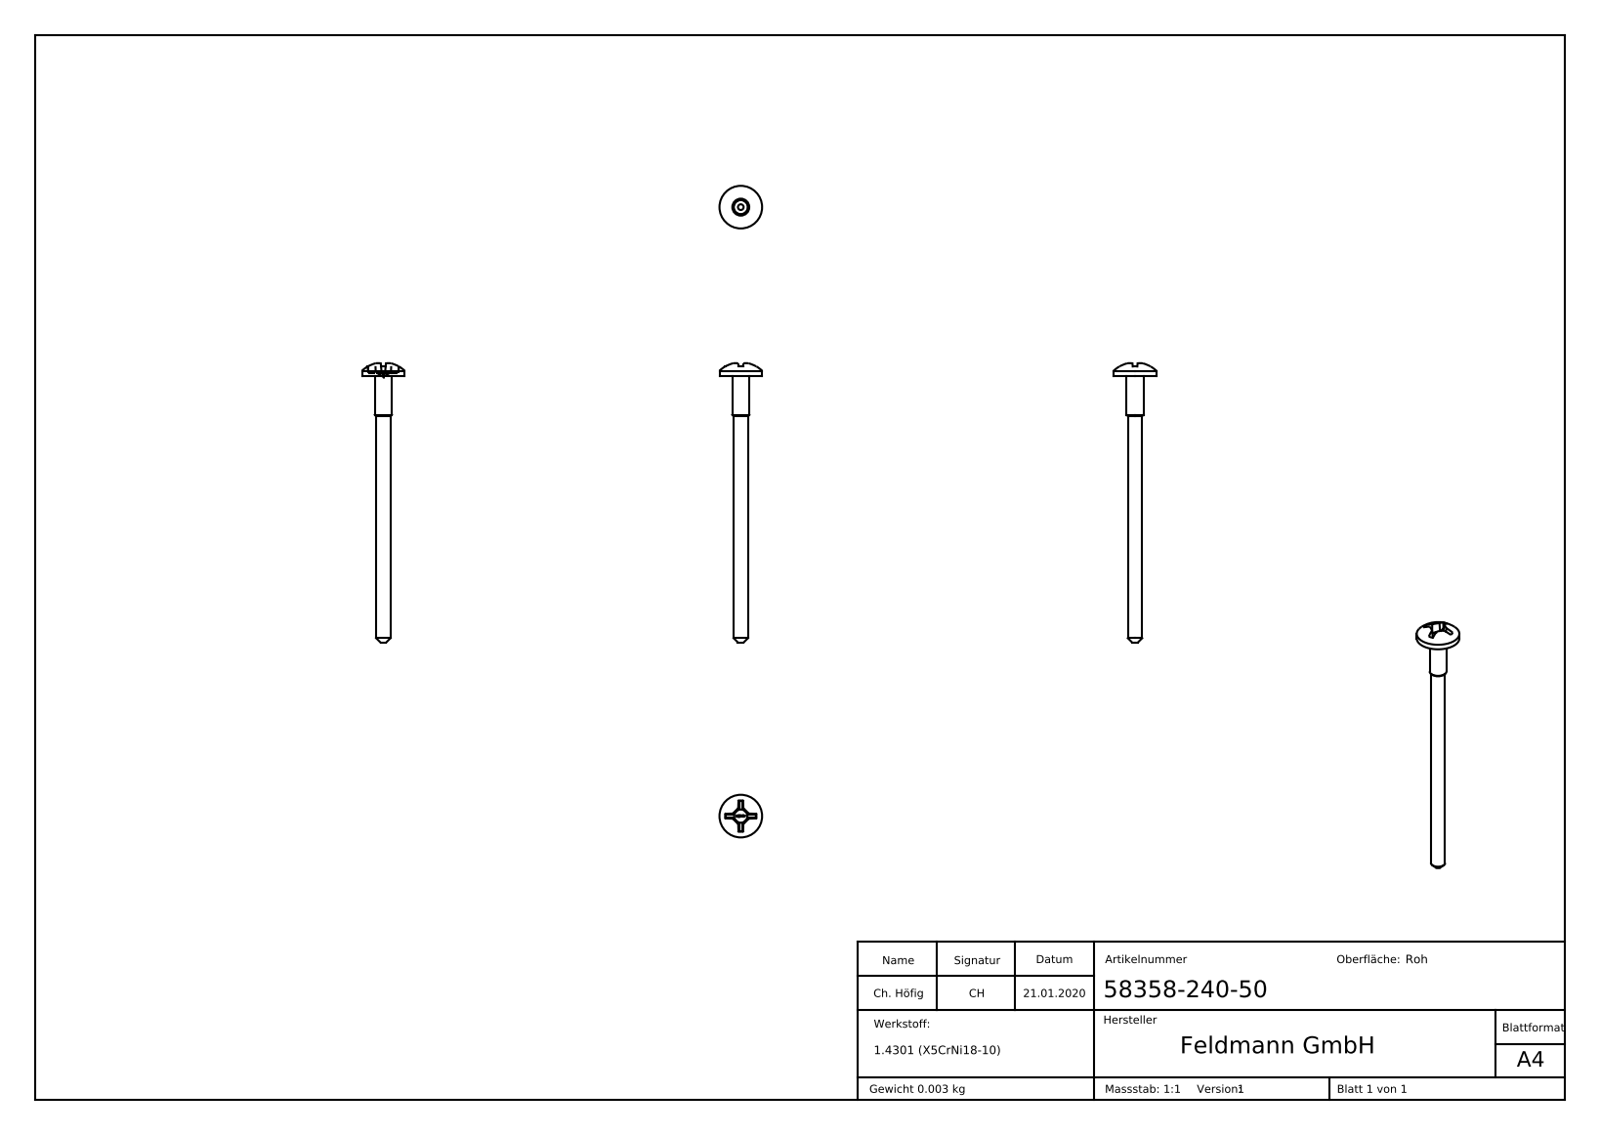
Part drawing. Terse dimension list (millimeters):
name: 58358-240-50
written by: SolidWorks 2015 (CONFIG_CONTROL_DESIGN)
unit: mm
bodies: 1 solid, 326 faces (121 planar, 3 cylindrical, 202 other)
size: 52.43 × 8 × 8
volume: 368 mm³; area: 584 mm²
bosses: 1× ⌀8, 1× ⌀3.18, 1× ⌀2.67
face distances: 0.6, 50, 50.6, 42.5, 7.5, 8.1, 0.32, 0.31, 0.33, 0.34
